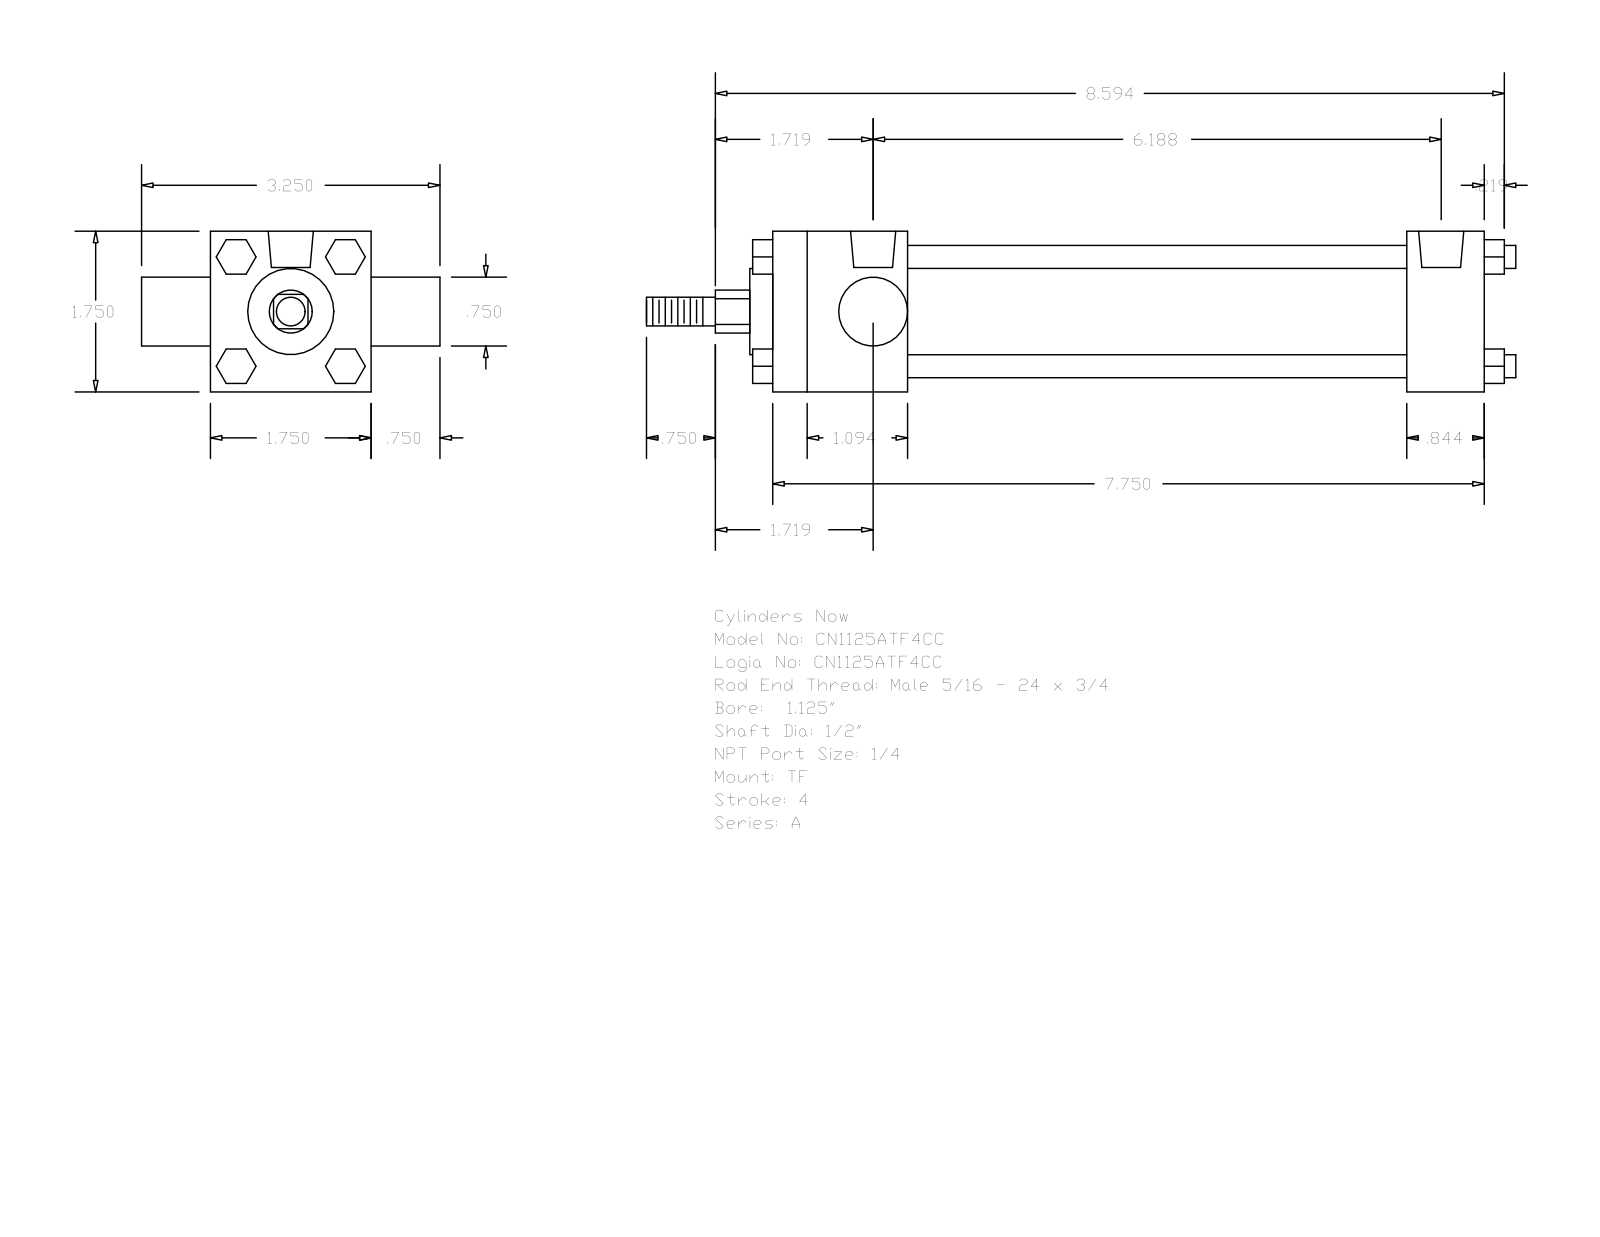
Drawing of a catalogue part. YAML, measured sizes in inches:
part_name: "A_TF__0112_0.5"
step_written_by: "GSSL Pune (CONFIG_CONTROL_DESIGN)"
units: inches
bodies: {solids: 0, faces: 120, planar: 92, cylindrical: 28, other: 0}
overall_size: [9.469, 3.25, 1.75]
round_holes:
  - {diameter: 0.219, count: 3}
  - {diameter: 0.492, count: 2}
round_bosses_or_shafts:
  - {diameter: 0.25, count: 4}
  - {diameter: 1.255, count: 1}
  - {diameter: 0.937, count: 1}
  - {diameter: 0.75, count: 1}
  - {diameter: 0.5, count: 1}
  - {diameter: 0.313, count: 1}
partial_cylinders:
  - {radius: 0.234, count: 1}
face_to_face_distances: [1.75, 7.75, 6.906, 0.844, 1.469, 5.437, 6.281, 0.75, 2.5, 0.375]
hole_center_spacings: [0.062, 0.063, 6.063, 6.125, 6.125, 6.187]
